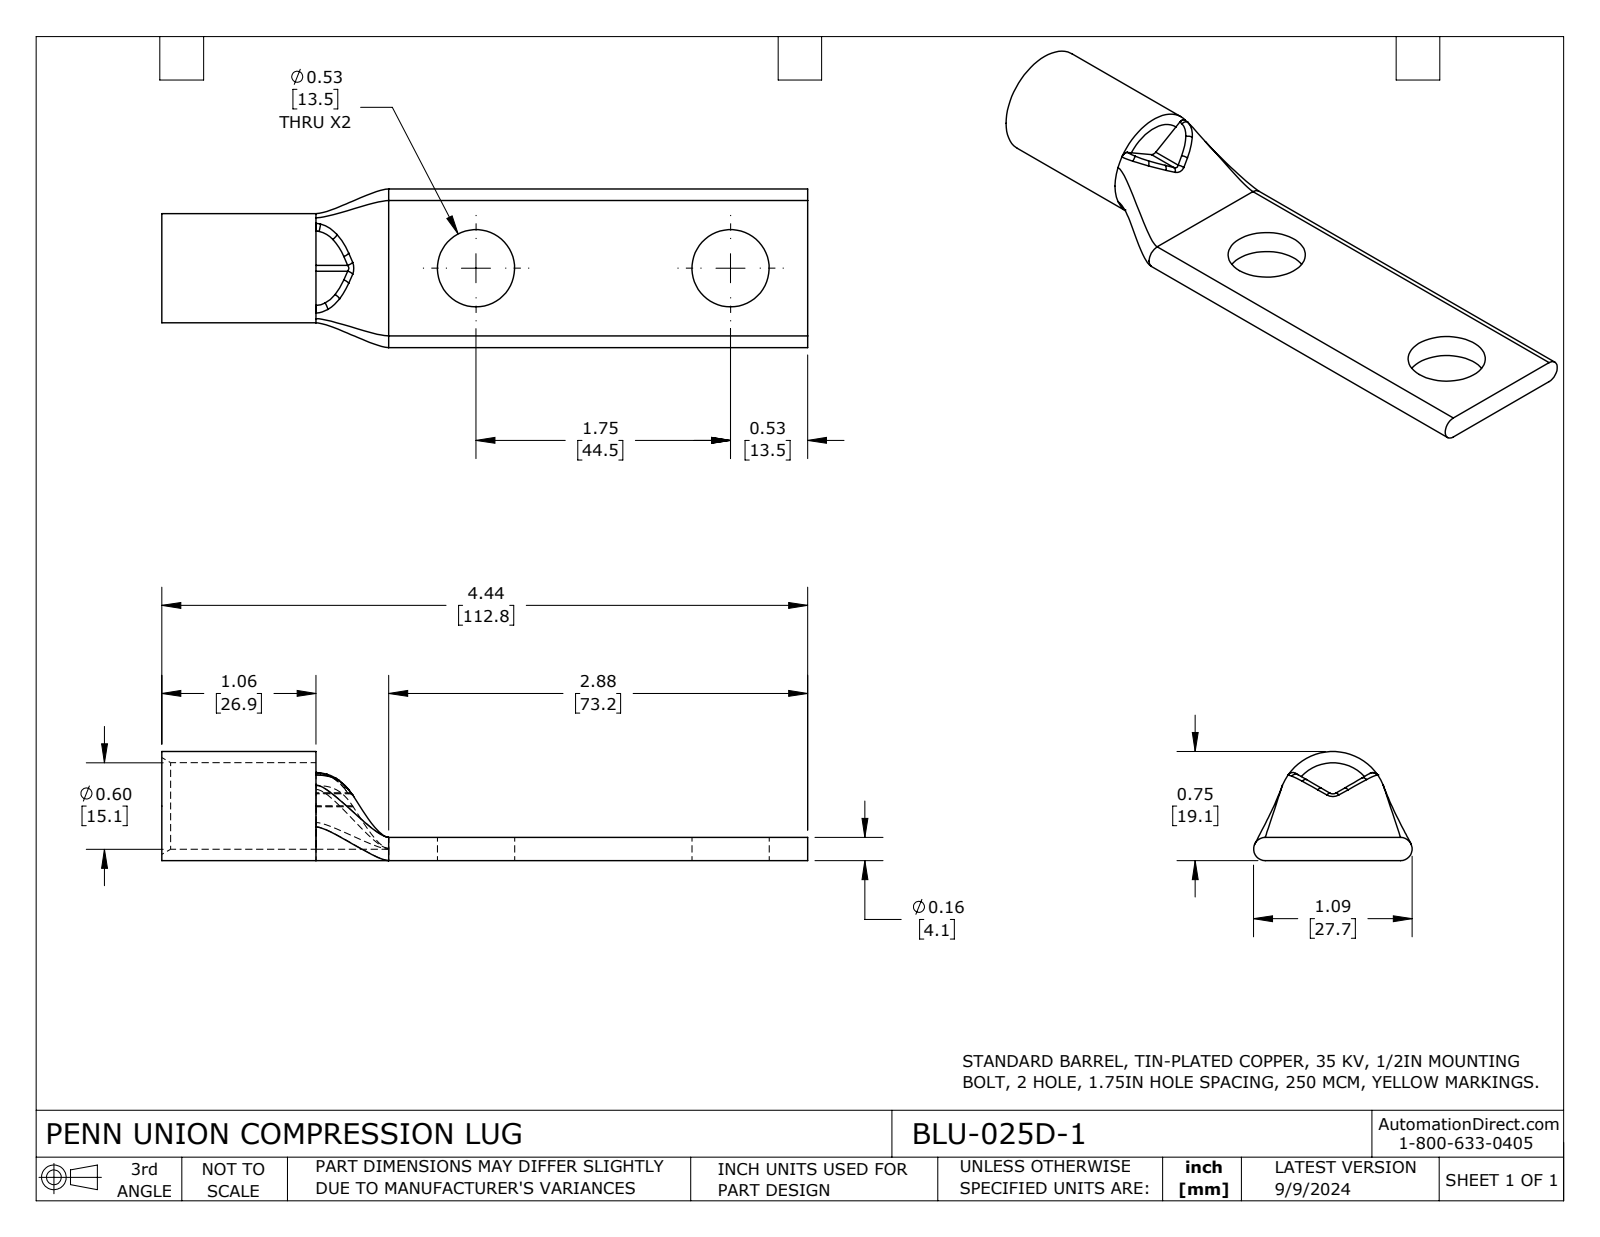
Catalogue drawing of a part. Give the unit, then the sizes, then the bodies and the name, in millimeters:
Units: millimetres
Overall size (bounding box): 112.8 × 27.7 × 19.1
Round holes (diameter × count): ⌀13.5 ×2, ⌀15.1 ×1
Round bosses / shafts (diameter × count): ⌀19.1 ×1
Partial cylindrical surfaces — rounded edges, fillets, slot ends (radius × count): R1 ×2, R2 ×2
Main face-to-face distances: 4.1, 112.8, 26.9, 85.9, 2, 39.6, 12.7, 73.2
Hole centre spacings: 44.5
Volume: 10 900 mm³ · Surface area: 8 819 mm²
Bodies: 1 solid, 45 faces (11 planar, 13 cylindrical, 21 other)
Part name (STEP PRODUCT): BLU-025D-1
STEP written by: SolidWorks 2023 (CONFIG_CONTROL_DESIGN)
